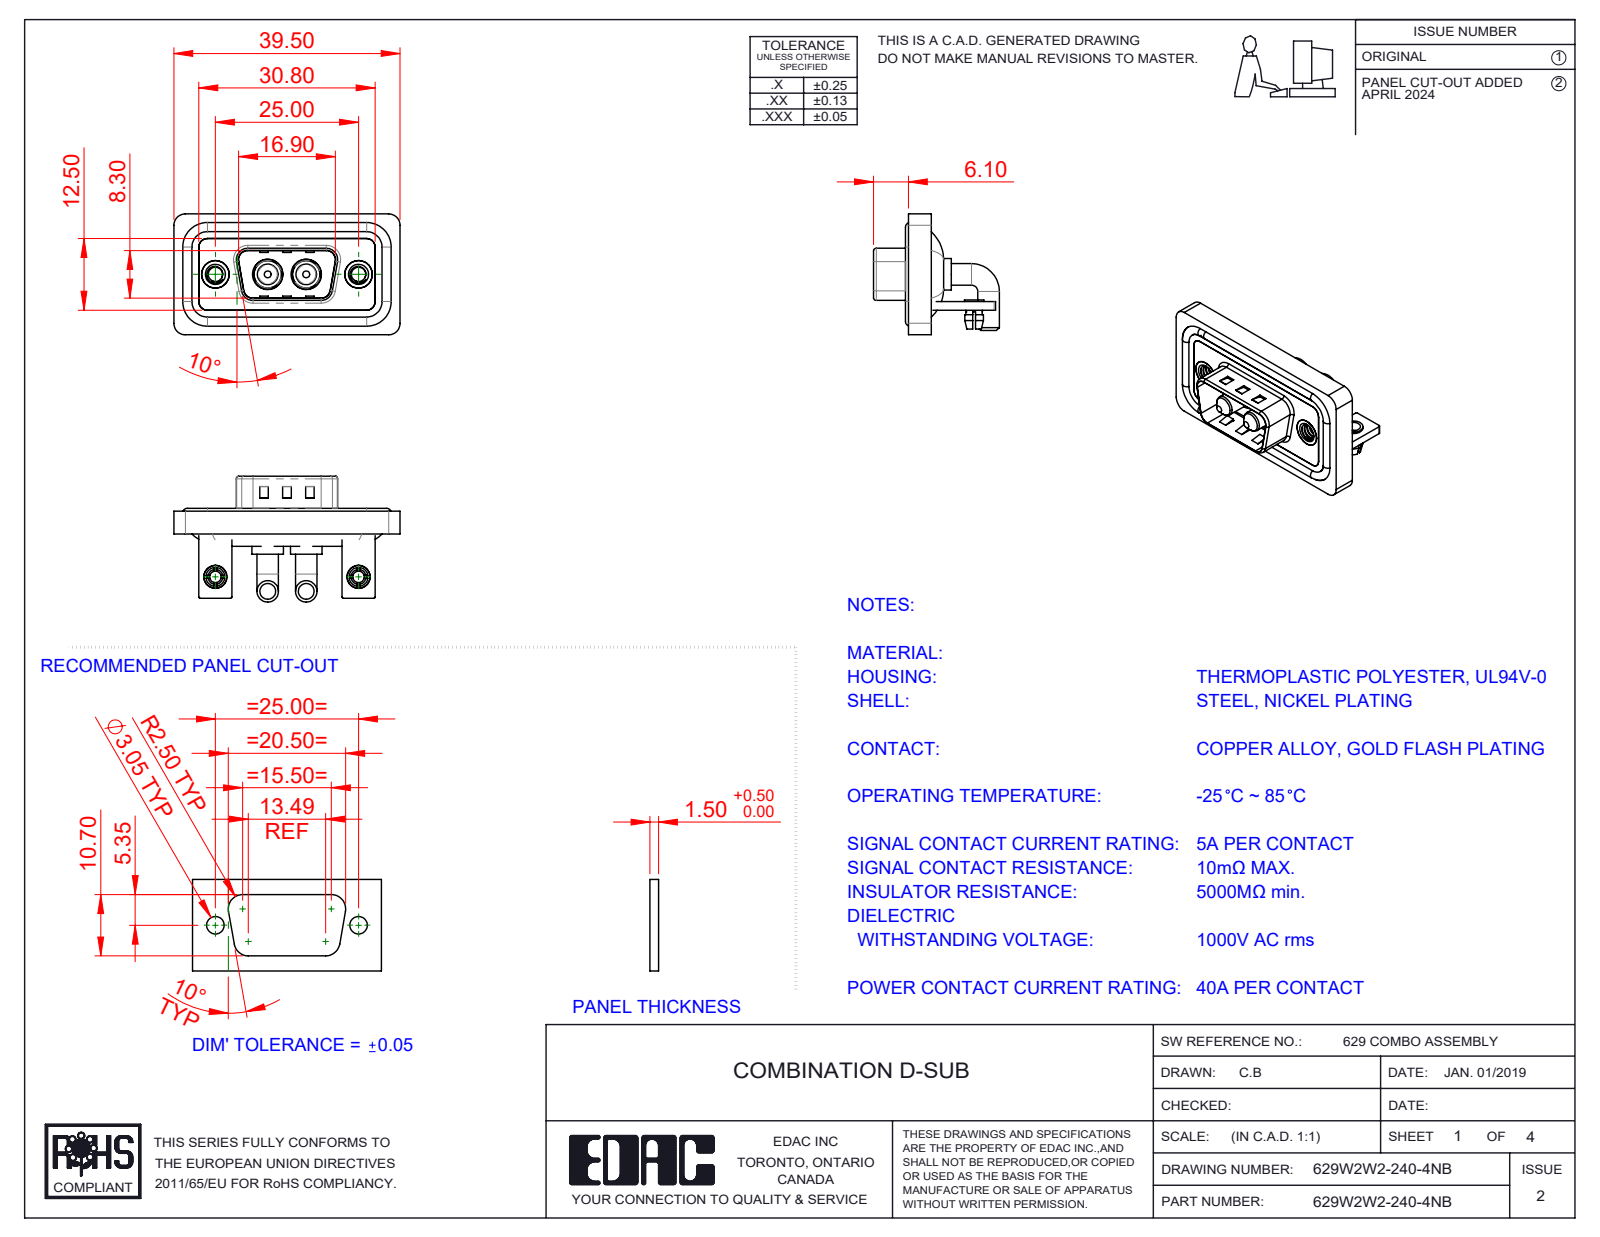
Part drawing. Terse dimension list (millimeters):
name: Power Pin_40A RA; 629Combo Board Lock; 629Combo Shell Front_09 Contacts; 629Combo Threaded Rivet_B (+5 more)
written by: SolidWorks 2023 (CONFIG_CONTROL_DESIGN)
unit: mm
bodies: 15 solids, 627 faces (233 planar, 272 cylindrical, 122 other)
size: 39.5 × 21.98 × 21.1
volume: 5 038 mm³; area: 8 054 mm²
holes: 4× ⌀2.5, 2× ⌀2, 2× ⌀3.2, 2× ⌀4, 2× ⌀4.8, 2× ⌀4.85, 2× ⌀5, 2× ⌀5.3
bosses: 4× ⌀3.75, 4× ⌀1.6, 2× ⌀5.5, 2× ⌀5.2, 2× ⌀4.9, 2× ⌀4.75, 2× ⌀4, 2× ⌀3.6
rounds: 19× R2, 18× R1.5, 16× R0.25, 9× R0.5, 8× R1.6, 4× R0.6, 4× R0.65, 4× R0.9
face distances: 0.4, 1.5, 2.9, 0.8, 1.1, 1.2, 2.1, 1.6, 3.7, 2.5
hole spacings: 9.14, 15.86, 25, 6.72
